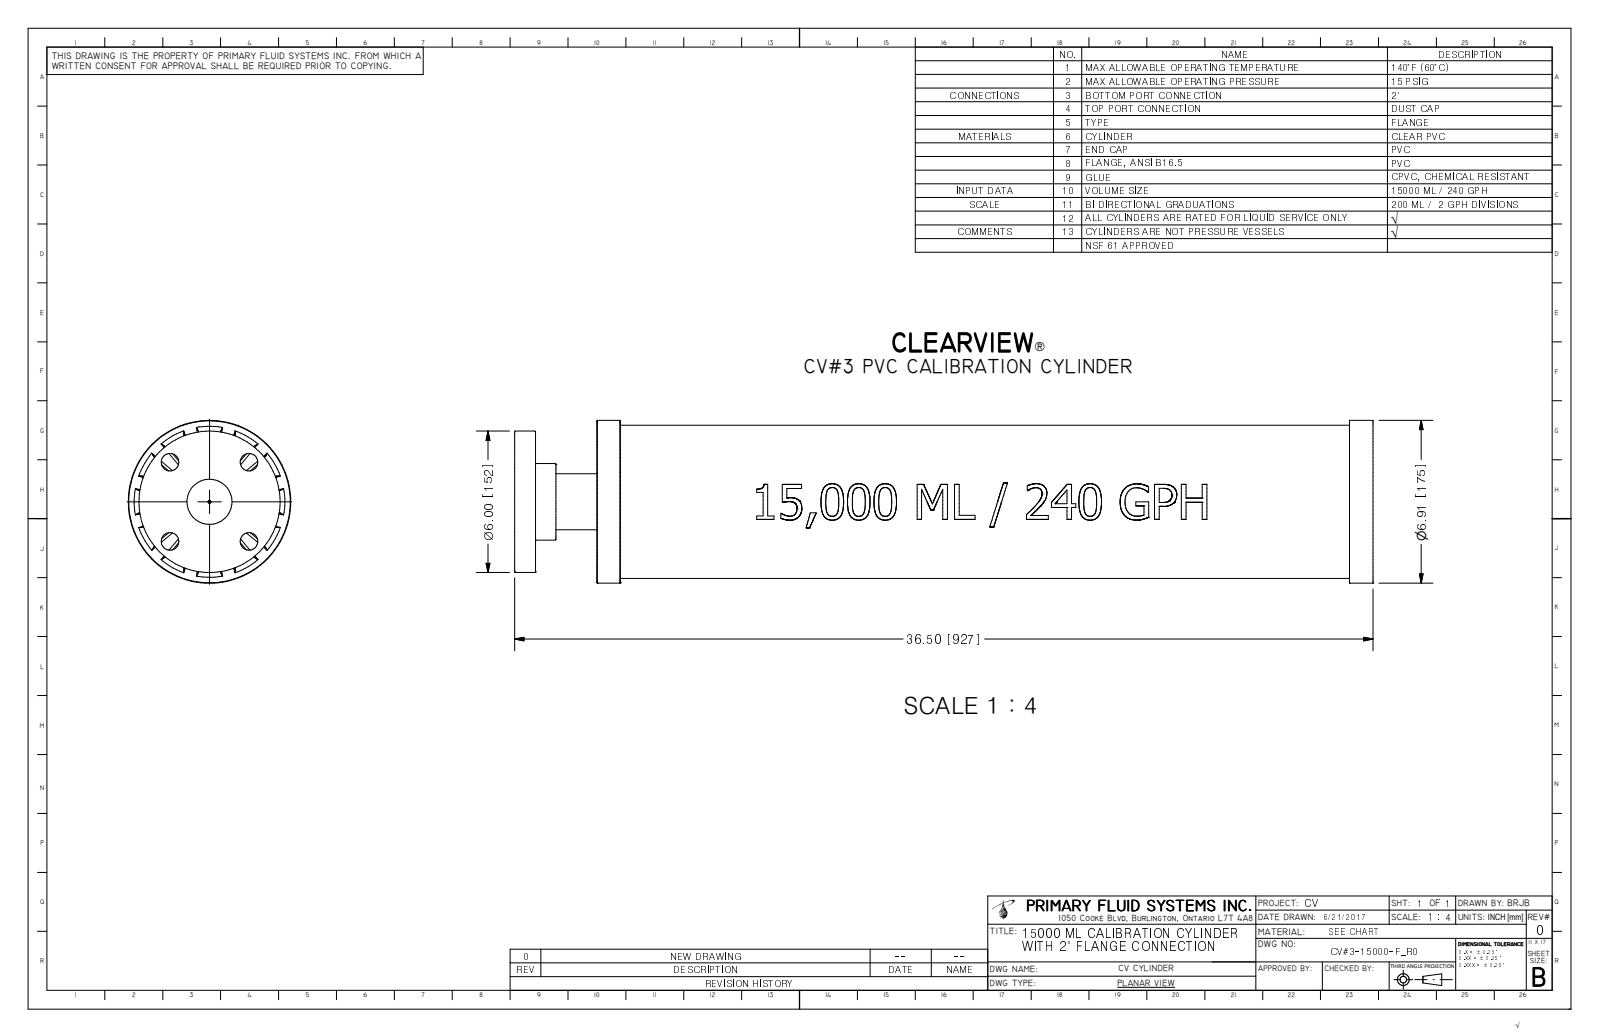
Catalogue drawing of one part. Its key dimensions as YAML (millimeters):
part_name: "PV#3-15000-F_R0"
step_written_by: "Autodesk Inventor 2009 (AUTOMOTIVE_DESIGN)"
units: millimeters
bodies: {solids: 1, faces: 330, planar: 114, cylindrical: 35, other: 181}
overall_size: [927.1, 175.4, 175.4]
volume: 2429000
surface_area: 1070000
round_holes:
  - {diameter: 18.9, count: 4}
  - {diameter: 48.6, count: 1}
  - {diameter: 49.3, count: 1}
  - {diameter: 160.5, count: 1}
round_bosses_or_shafts:
  - {diameter: 175.4, count: 1}
  - {diameter: 165.1, count: 1}
  - {diameter: 152.4, count: 1}
  - {diameter: 82.4, count: 1}
  - {diameter: 60.3, count: 1}
partial_cylinders:
  - {radius: 82.5, count: 1}
face_to_face_distances: [25.4, 901.7, 927.1, 22.5, 879.2, 904.6, 101.6, 79.1, 800.1, 825.5]
hole_center_spacings: [60.3, 85.3, 120.7]
